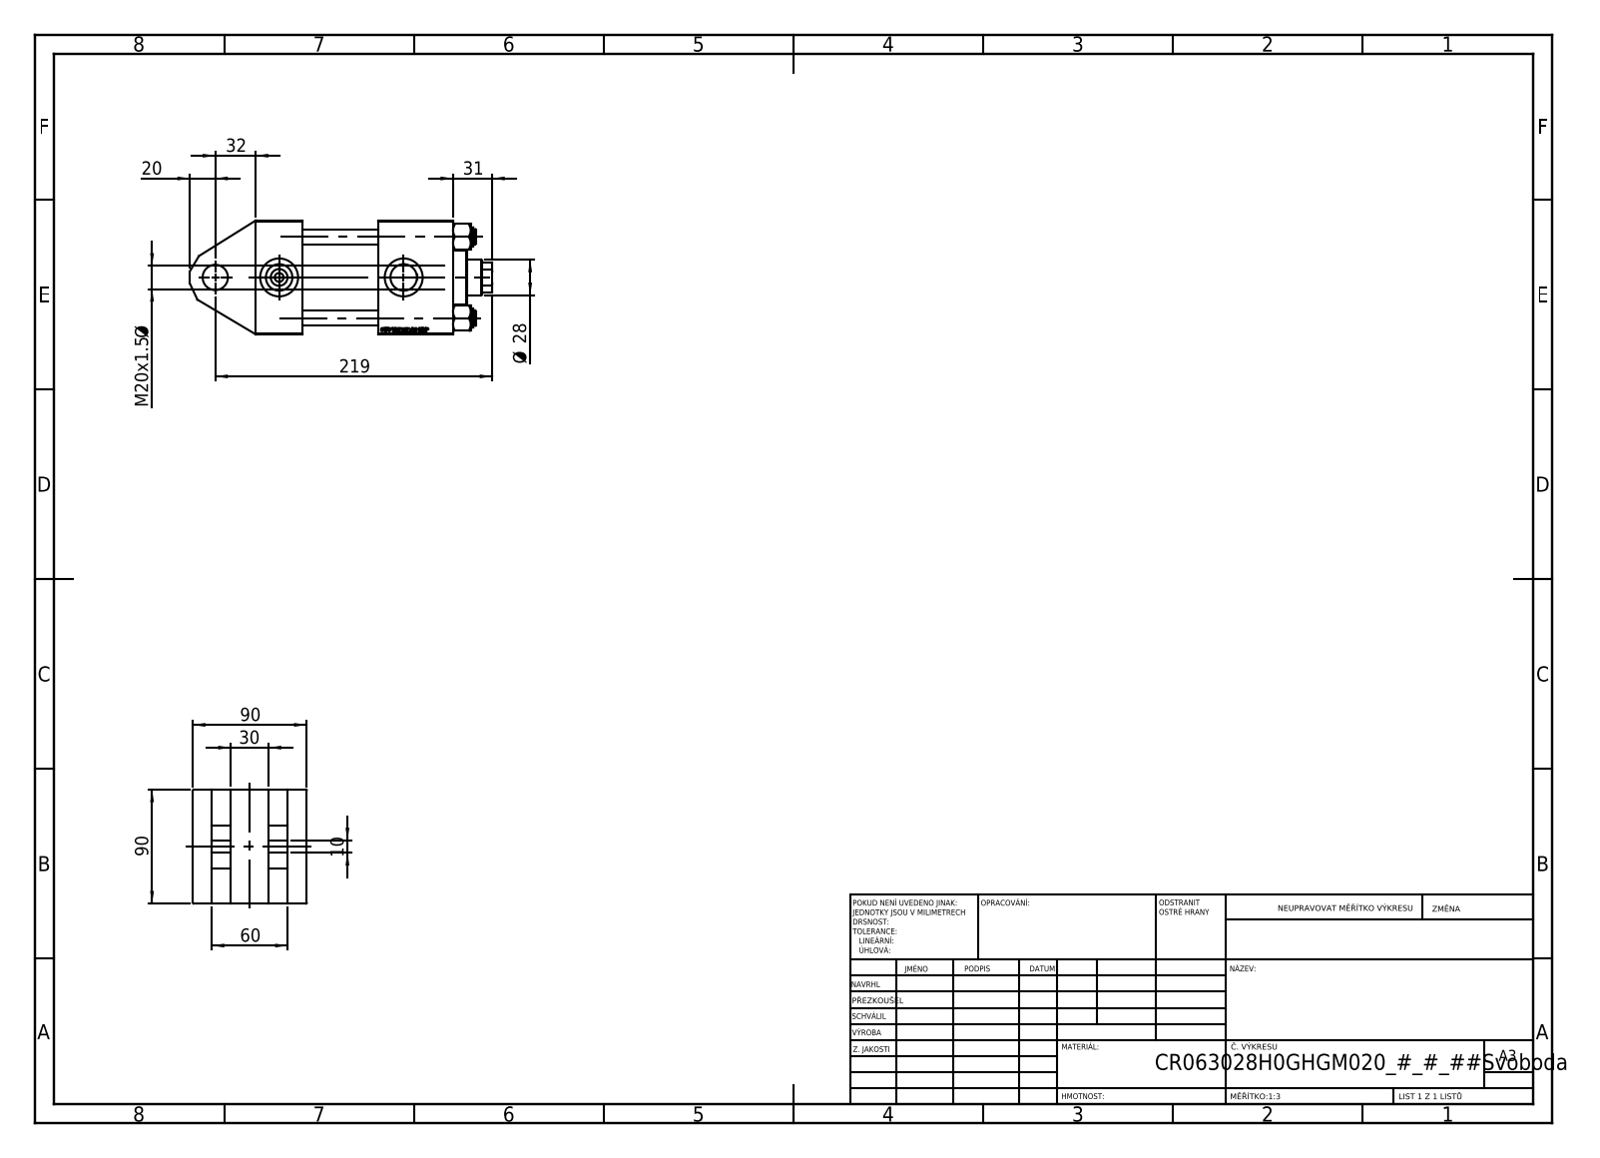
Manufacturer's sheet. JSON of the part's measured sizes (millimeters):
{"part_name": "V215CR_H_Body; V215_VC_A; NUT_M5_H; V215CR_TYCINKA_H (+1 more)", "step_written_by": "SolidWorks 2019 (CONFIG_CONTROL_DESIGN)", "units": "millimeters", "bodies": {"solids": 11, "faces": 1129, "planar": 518, "cylindrical": 83, "other": 528}, "overall_size": [239, 90, 90], "volume_mm3": 1040000, "surface_area_mm2": 197060, "round_holes": [[12, 4], [7, 2], [20.96, 2], [30, 2], [18.5, 1], [20, 1], [28, 1], [31, 1], [50, 1], [60, 1], [63, 1]], "round_bosses_or_shafts": [[15, 4], [69, 1], [42, 1]], "partial_cylinders_radius": [[13.5, 1]], "face_to_face_distances": [90, 60, 15, 30, 119, 75, 37, 156, 45, 97], "hole_center_spacings": [45.47, 64.3, 90.93, 50.5, 98.5, 149]}
